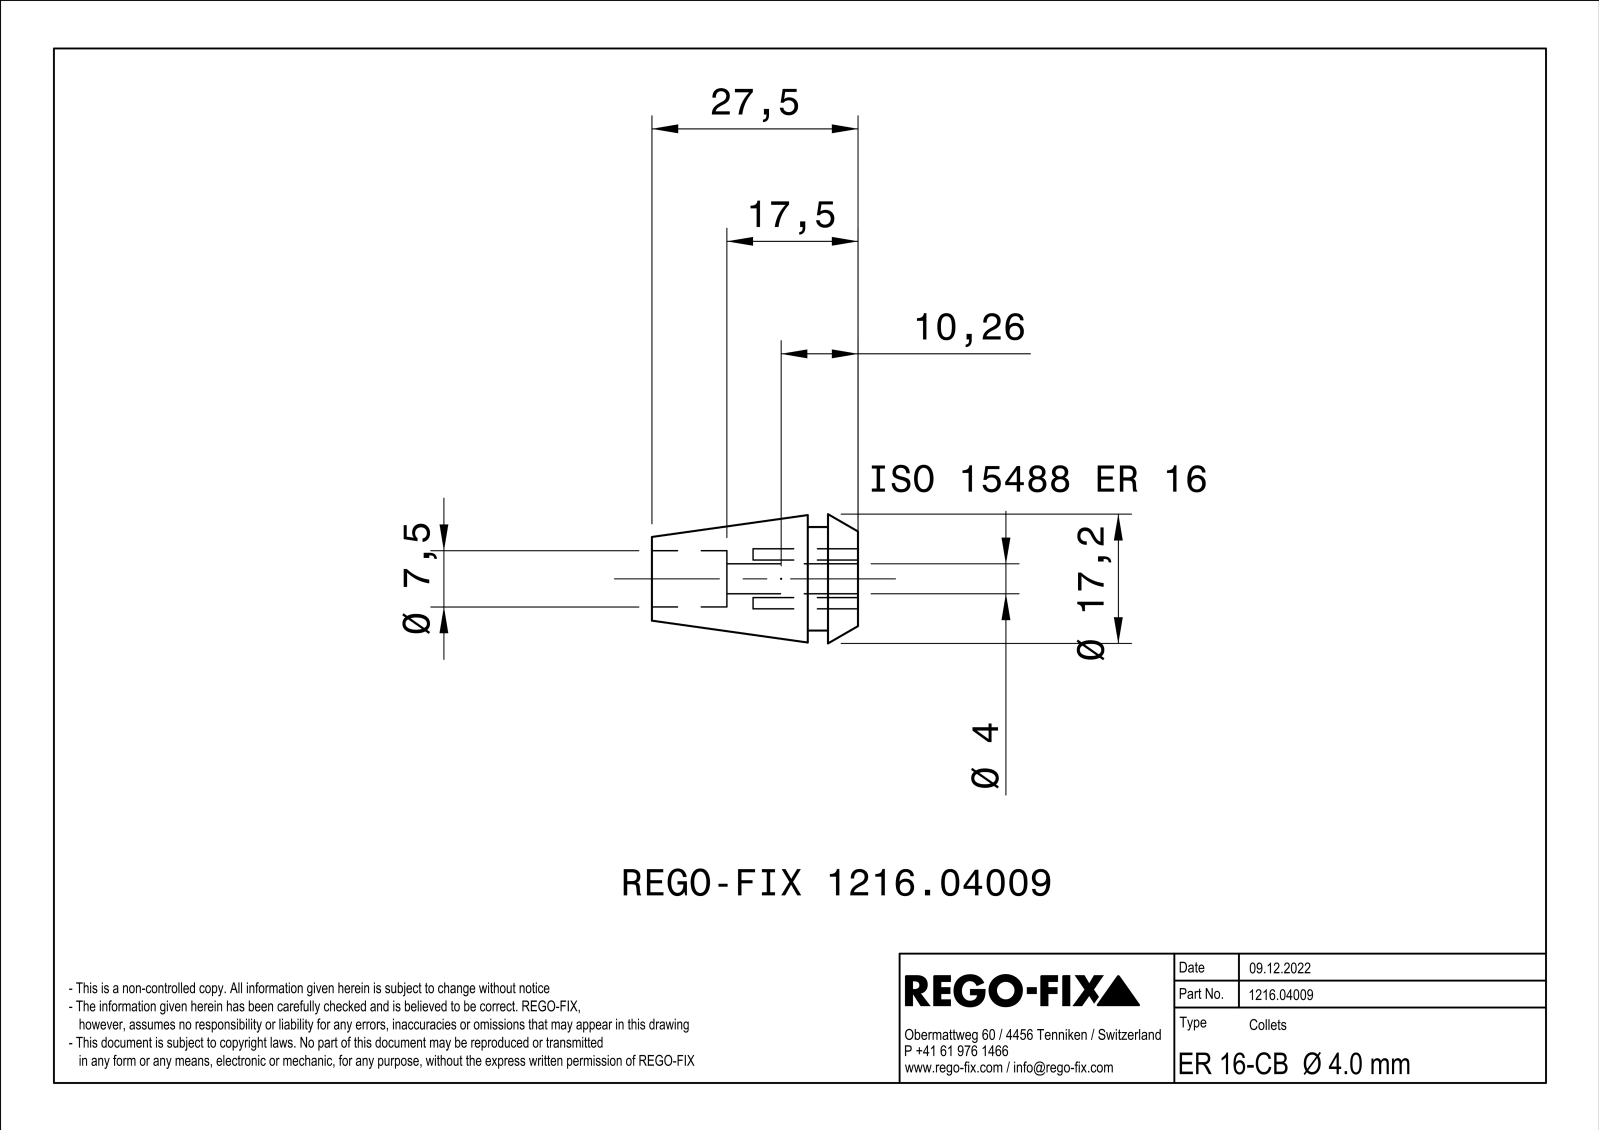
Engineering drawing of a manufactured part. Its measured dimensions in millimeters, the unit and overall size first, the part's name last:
Units: millimetres
Overall size (bounding box): 27.5 × 16.9 × 16.9
Round holes (diameter × count): ⌀1.5 ×4, ⌀4 ×1, ⌀7.5 ×1
Round bosses / shafts (diameter × count): ⌀16.74 ×1, ⌀13.8 ×1
Main face-to-face distances: 0.5, 4, 6.7, 2.7, 27.5, 23.5, 20.8, 22.5, 18.5, 15.8
Hole centre spacings: 3.25, 4.6, 6.51
Volume: 3 443 mm³ · Surface area: 3 444 mm²
Bodies: 1 solid, 118 faces (36 planar, 17 cylindrical, 65 other)
Part name (STEP PRODUCT): NOCUT
STEP written by: SIEMENS PLM Software Solid Edge ST10 (AUTOMOTIVE_DESIGN)
